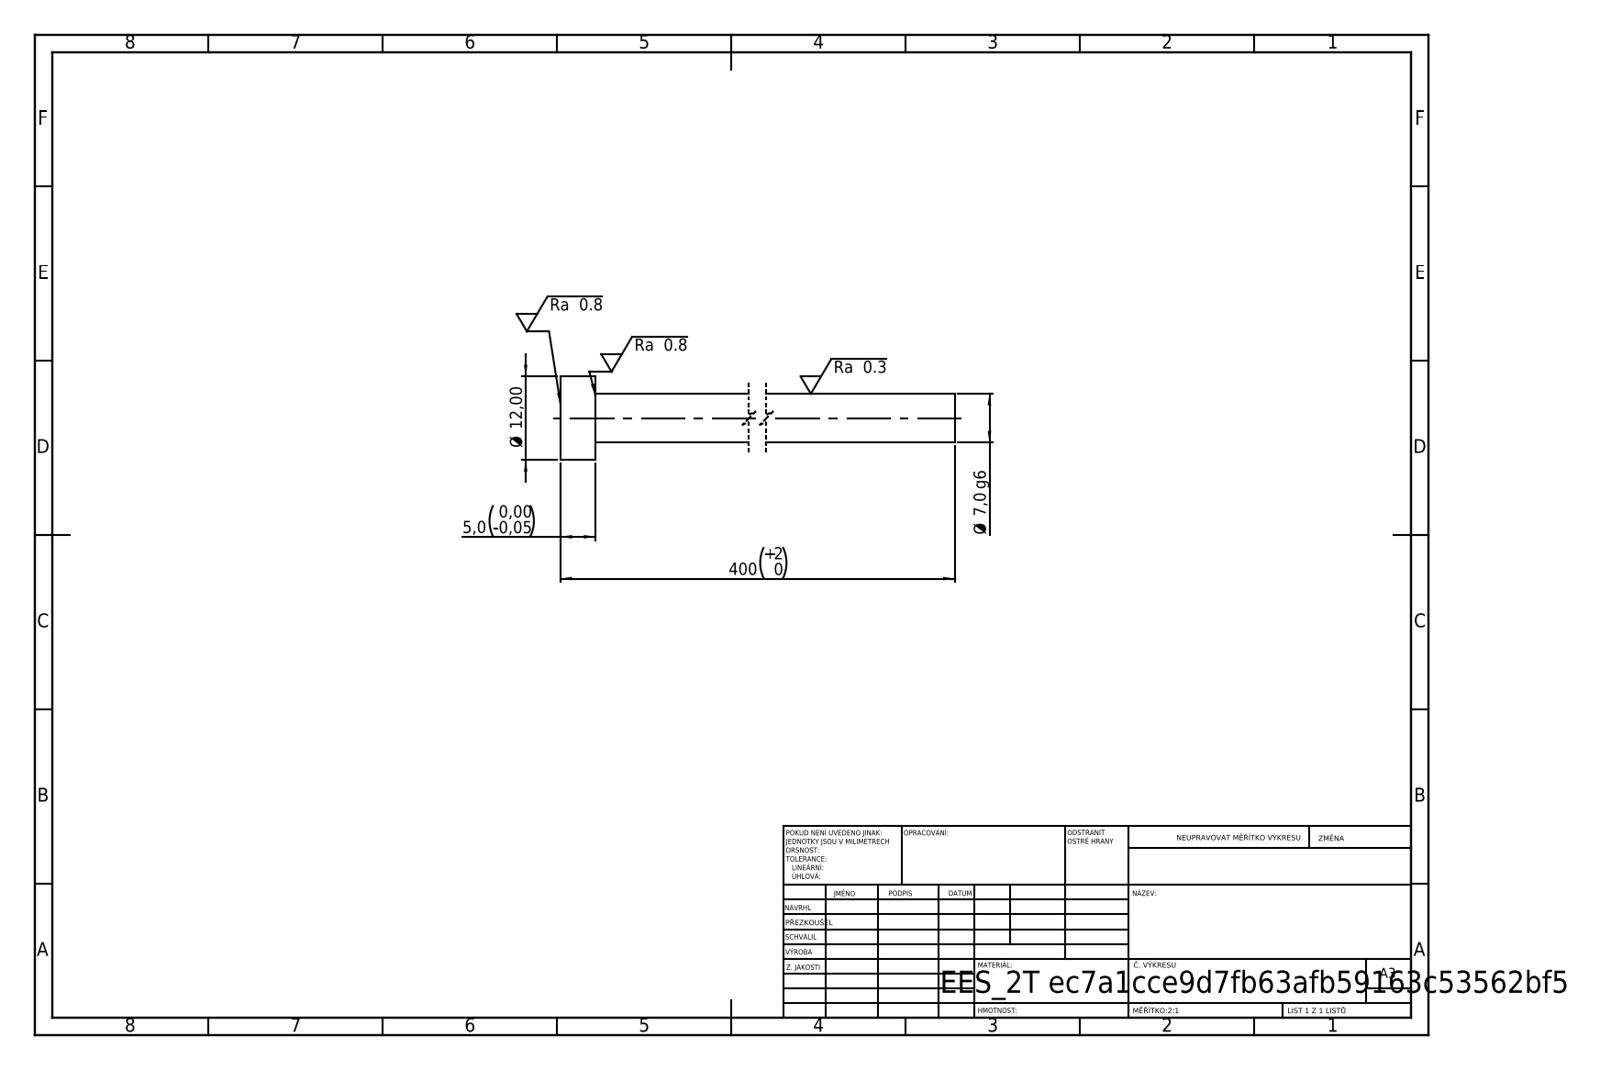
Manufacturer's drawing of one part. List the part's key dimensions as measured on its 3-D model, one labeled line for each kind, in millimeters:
STEP written by: SolidWorks 2019 (CONFIG_CONTROL_DESIGN)
Units: millimetres
Bodies: 1 solid, 7 faces (3 planar, 4 cylindrical, 0 other)
Overall size (bounding box): 400 × 12 × 12
Volume: 15 767 mm³ · Surface area: 9 101 mm²
Round bosses / shafts (diameter × count): ⌀12 ×1, ⌀7 ×1
Main face-to-face distances: 5, 400, 395
